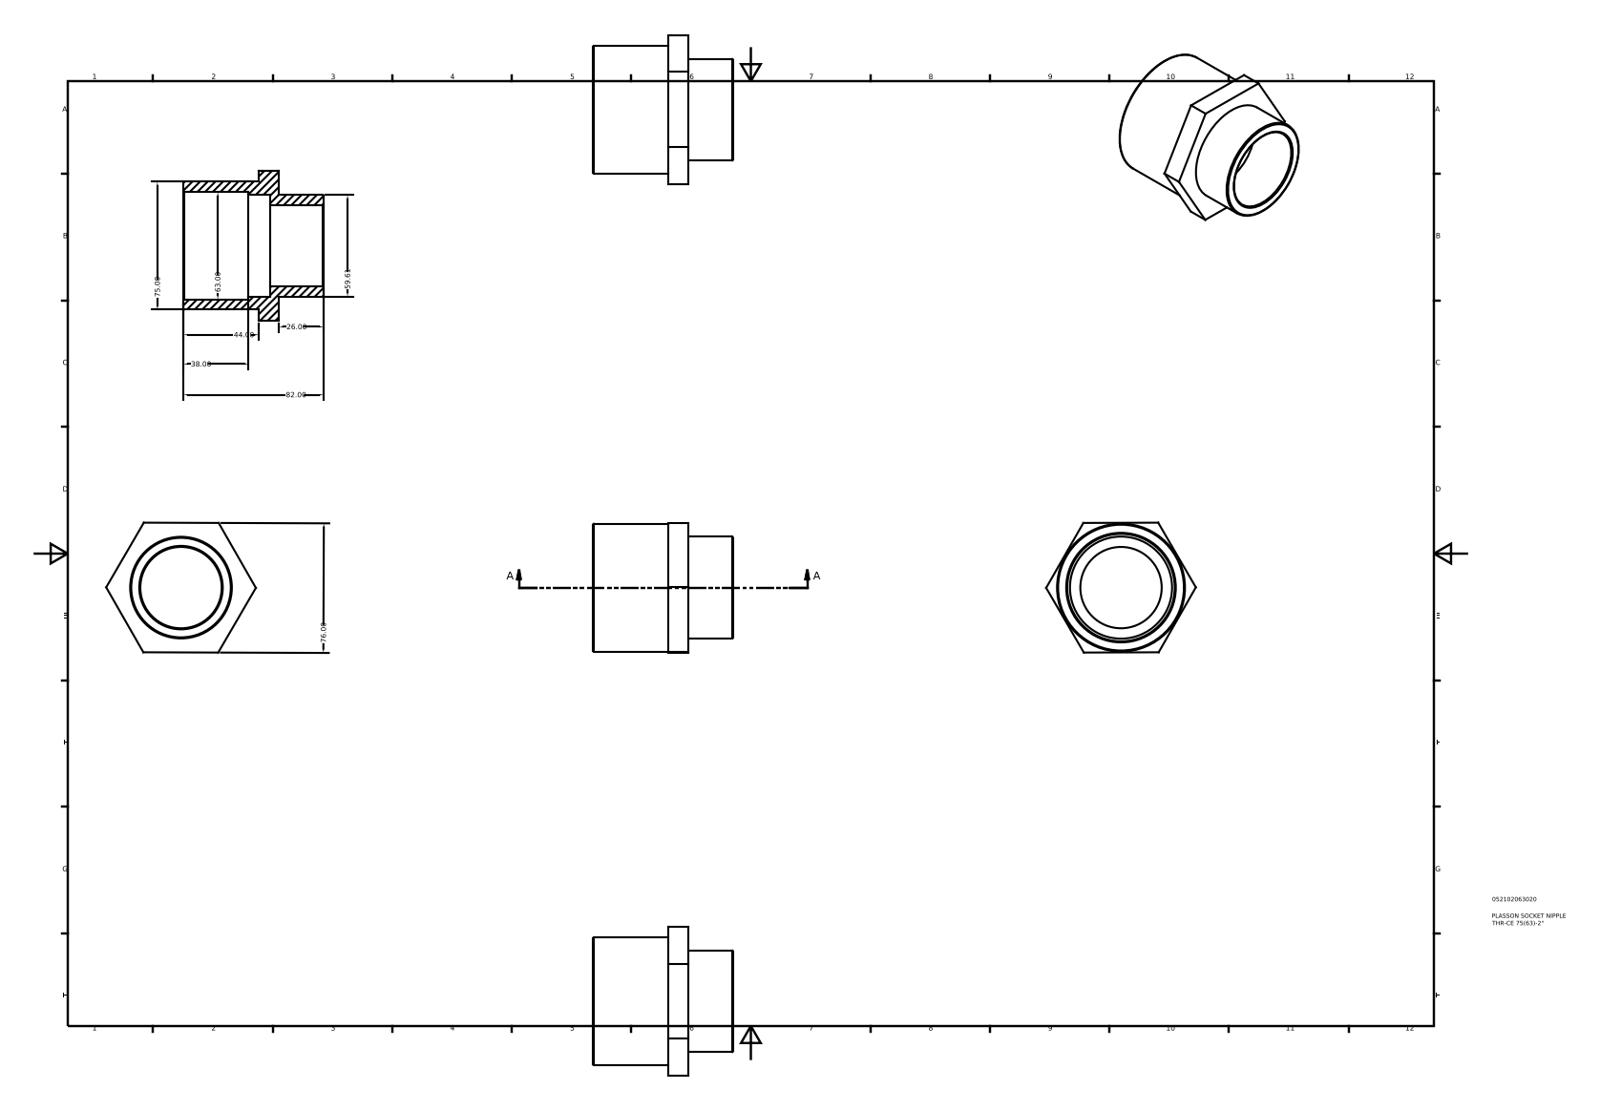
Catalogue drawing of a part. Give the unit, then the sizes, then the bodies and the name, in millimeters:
Units: millimetres
Overall size (bounding box): 87.76 × 82 × 76.16
Round holes (diameter × count): ⌀47.69 ×1, ⌀59.85 ×1, ⌀63 ×1
Round bosses / shafts (diameter × count): ⌀75 ×1, ⌀59.61 ×1
Main face-to-face distances: 56, 50.8, 5.2, 38, 44, 82, 31.2, 26, 6.8, 12
Volume: 116 717 mm³ · Surface area: 39 221 mm²
Bodies: 1 solid, 21 faces (12 planar, 5 cylindrical, 4 other)
Part name (STEP PRODUCT): 052102063020
STEP written by: Autodesk Inventor 2015 (AUTOMOTIVE_DESIGN)
